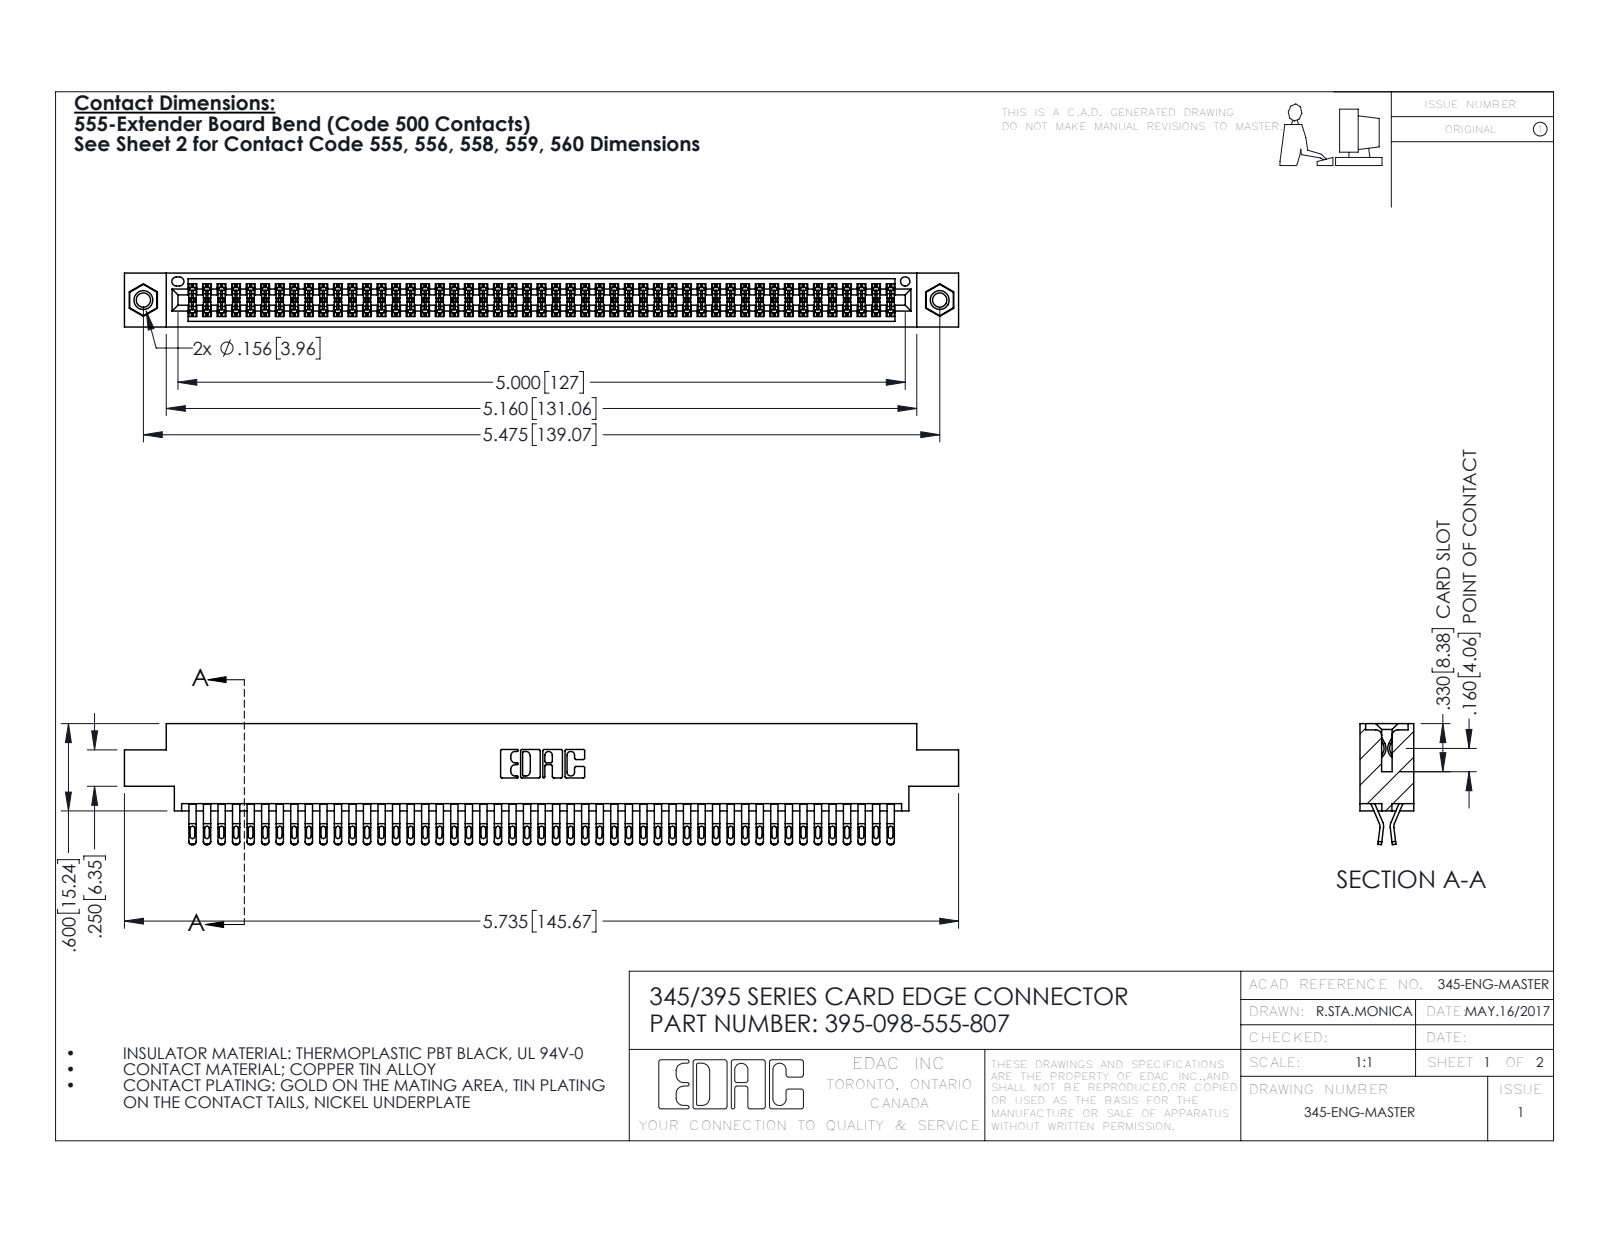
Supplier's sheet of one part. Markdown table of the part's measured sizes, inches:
| quantity | value |
| --- | --- |
| part name | 345-292-001_555 Tail; 395-098-555-807; 345-250-001_345-250-005-103; 345 Part_0.170 Offset - 0.156 Dia-TI |
| STEP written by | SolidWorks 2016 (CONFIG_CONTROL_DESIGN) |
| units | inches |
| bodies | 101 solids, 5678 faces (3154 planar, 2508 cylindrical, 16 other) |
| overall size | 5.735 × 0.832 × 0.37 |
| volume | 0.877 in³ |
| surface area | 34.94 in² |
| round holes (diameter × count) | 0.098 × 2, 0.125 × 2, 0.156 × 2, 0.064 × 1 |
| round bosses / shafts (diameter × count) | 0.155 × 2 |
| partial cylindrical surfaces (radius × count) | 0.016 × 245, 0.02 × 196, 0.006 × 147, 0.01 × 22, 0.007 × 6, 0.031 × 6, 0.026 × 3, 0.01 × 2 |
| main face-to-face distances | 0.072, 0.298, 0.37, 0.025, 0.2, 0.098, 0.272, 0.225, 0.175, 0.149 |
| hole center spacings | 0.27, 5.239, 5.475 |
